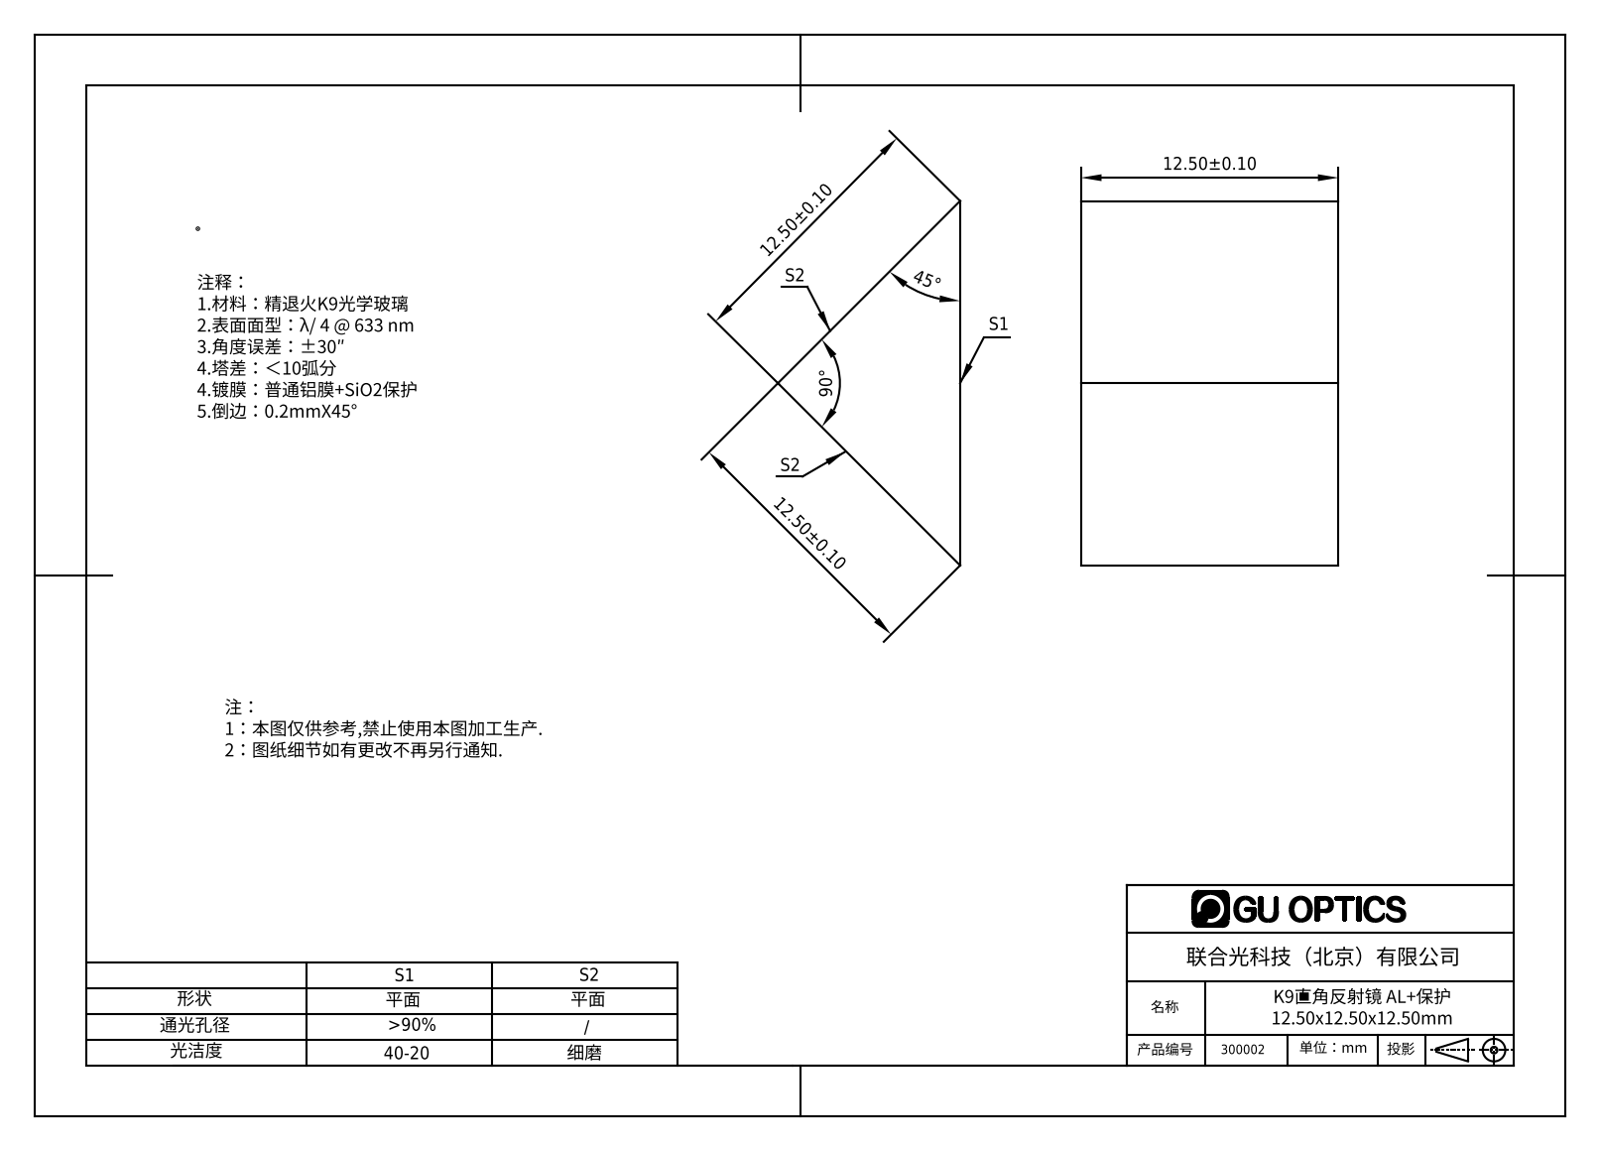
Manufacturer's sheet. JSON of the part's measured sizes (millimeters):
{"part_name": "30002", "step_written_by": "SolidWorks 2016 (AUTOMOTIVE_DESIGN)", "units": "millimeters", "bodies": {"solids": 1, "faces": 5, "planar": 5, "cylindrical": 0, "other": 0}, "overall_size": [17.68, 12.5, 8.84], "volume_mm3": 977, "surface_area_mm2": 690, "face_to_face_distances": [12.5]}
